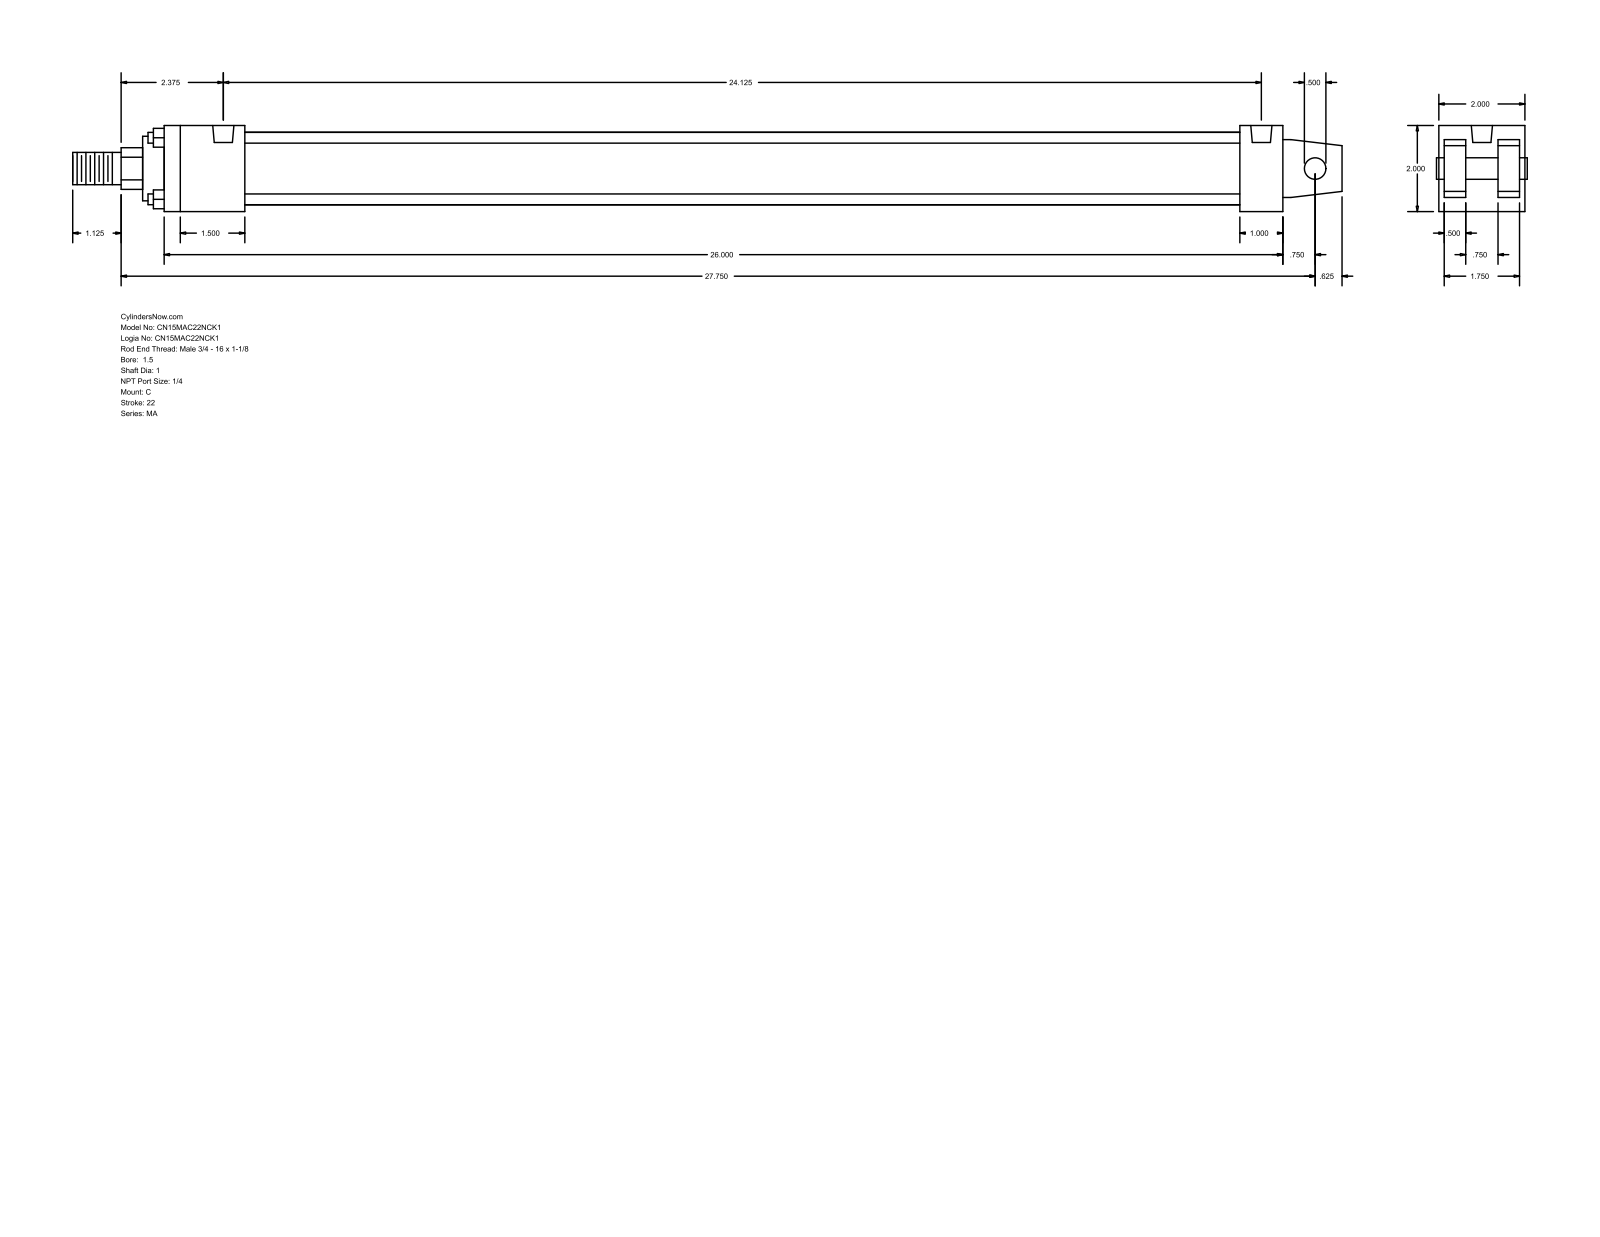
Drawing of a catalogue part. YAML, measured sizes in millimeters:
part_name: "MA_C__0150_1"
step_written_by: "GSSL Pune (CONFIG_CONTROL_DESIGN)"
units: millimeters
bodies: {solids: 0, faces: 103, planar: 76, cylindrical: 27, other: 0}
overall_size: [749.3, 50.8, 50.8]
round_holes:
  - {diameter: 7.94, count: 4}
  - {diameter: 12.49, count: 2}
round_bosses_or_shafts:
  - {diameter: 6.35, count: 4}
  - {diameter: 42.93, count: 1}
  - {diameter: 38.1, count: 1}
  - {diameter: 25.4, count: 1}
  - {diameter: 19.05, count: 1}
  - {diameter: 12.7, count: 1}
partial_cylinders:
  - {radius: 12.29, count: 1}
face_to_face_distances: [50.8, 47.63, 12.7, 34.93, 3.17, 15.87, 31.76, 60.33, 647.7, 660.4]
hole_center_spacings: [612.77]
